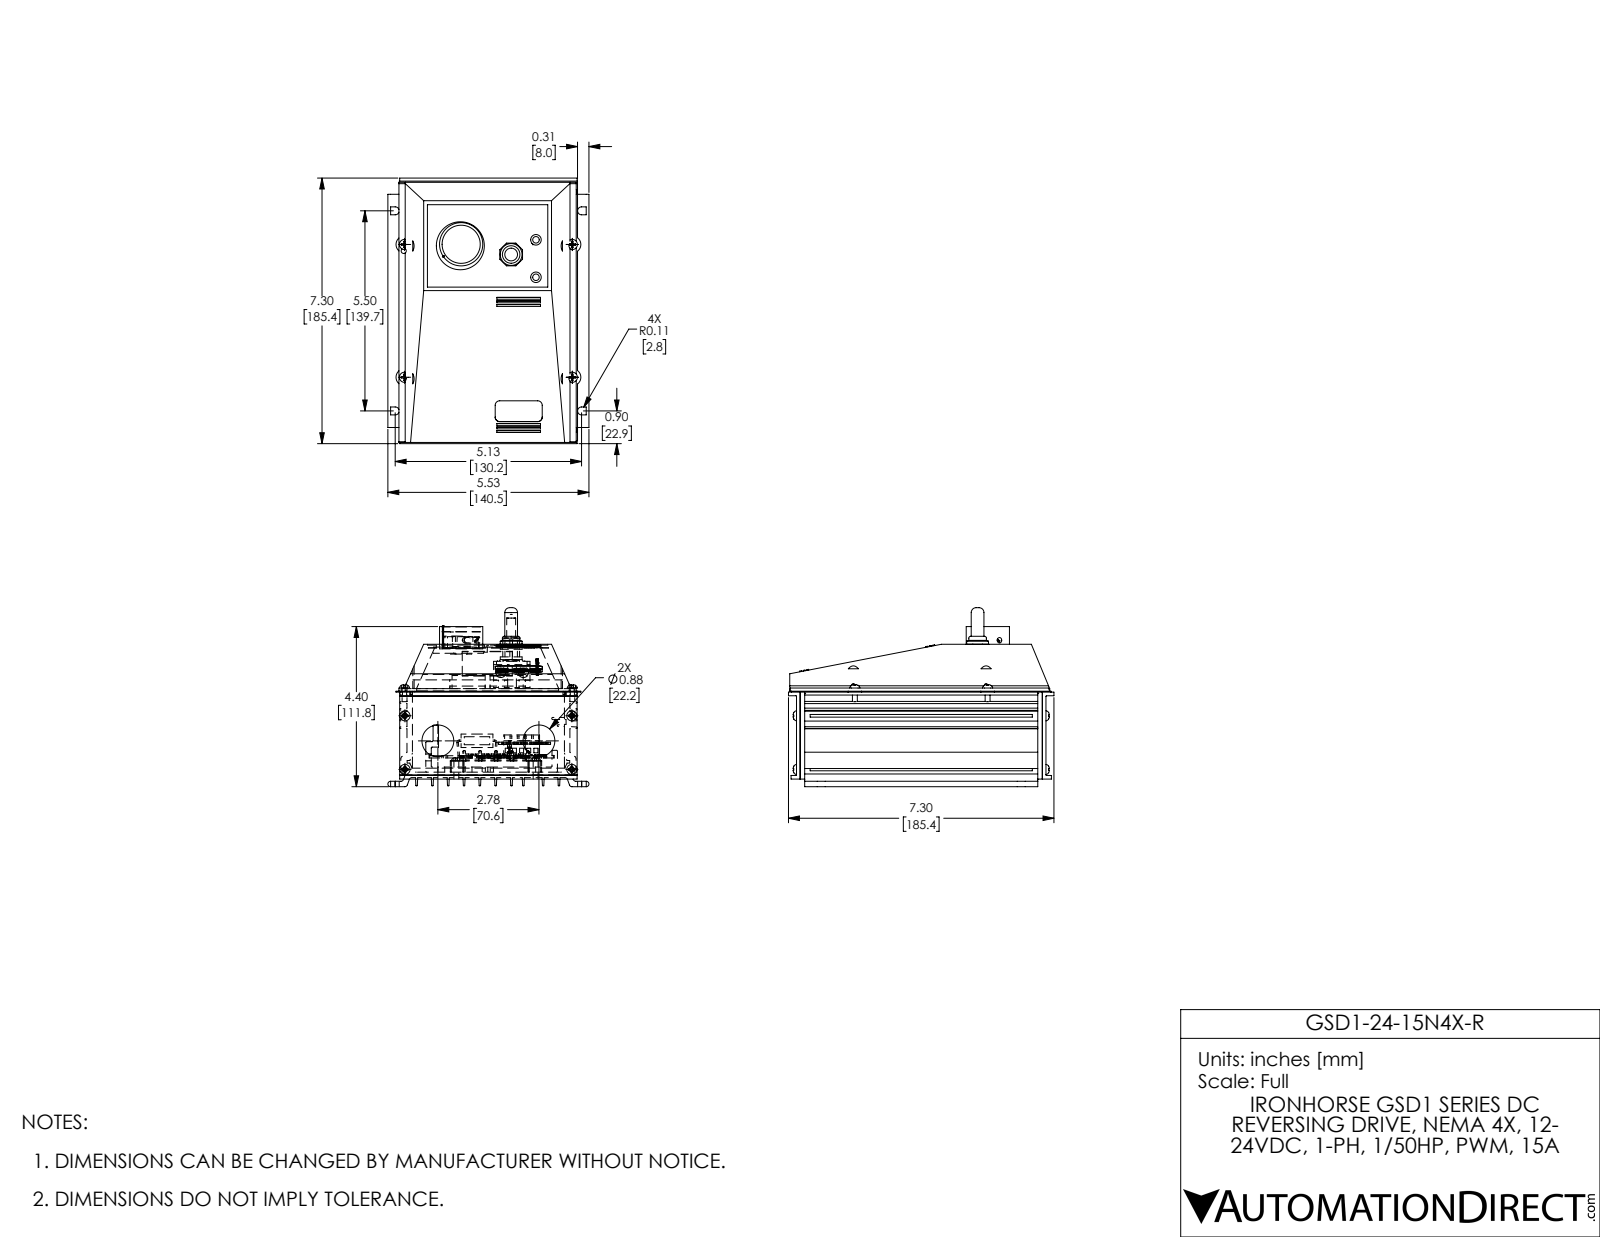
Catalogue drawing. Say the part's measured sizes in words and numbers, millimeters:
The part is named "GSD1-24-15N4X-R". Its 3-D file was written by "SolidWorks 2017 (AUTOMOTIVE_DESIGN)". It is 77 solids with 2810 faces: 1763 planar, 897 cylindrical and 150 other. Overall it measures 185.4 by 140.5 by 125 millimeters. Its volume is 518 800 cubic millimeters and its surface area 359 300 square millimeters. Round holes: 76 of diameter 0.8, 26 of diameter 1, 15 of diameter 0.9, 15 of diameter 1.2, 12 of diameter 3.6, 8 of diameter 1.1, 8 of diameter 2.6, 7 of diameter 0.9, 6 of diameter 1.3, 5 of diameter 0.9, 5 of diameter 4, 4 of diameter 1.4. Round bosses or shafts: 10 of diameter 3.4, 4 of diameter 8.5, 3 of diameter 8.4, 2 of diameter 7.4, 2 of diameter 6.6, 2 of diameter 1, 1 of diameter 37.6, 1 of diameter 30.2. Partial cylindrical surfaces (rounded edges, fillets, slot ends): 32 of radius 0.6, 19 of radius 0.5, 15 of radius 0.1, 14 of radius 3.2, 13 of radius 0.3, 10 of radius 1, 10 of radius 1.9, 8 of radius 0.1. The main face-to-face distances are 3.8, 6.4, 2.5, 13.7, 60.3, 56.5, 9.9, 1.6, 11, 8. The hole center spacings are 5, 12.7, 14, 4, 6.2, 6.4, 27.9, 2.7.
